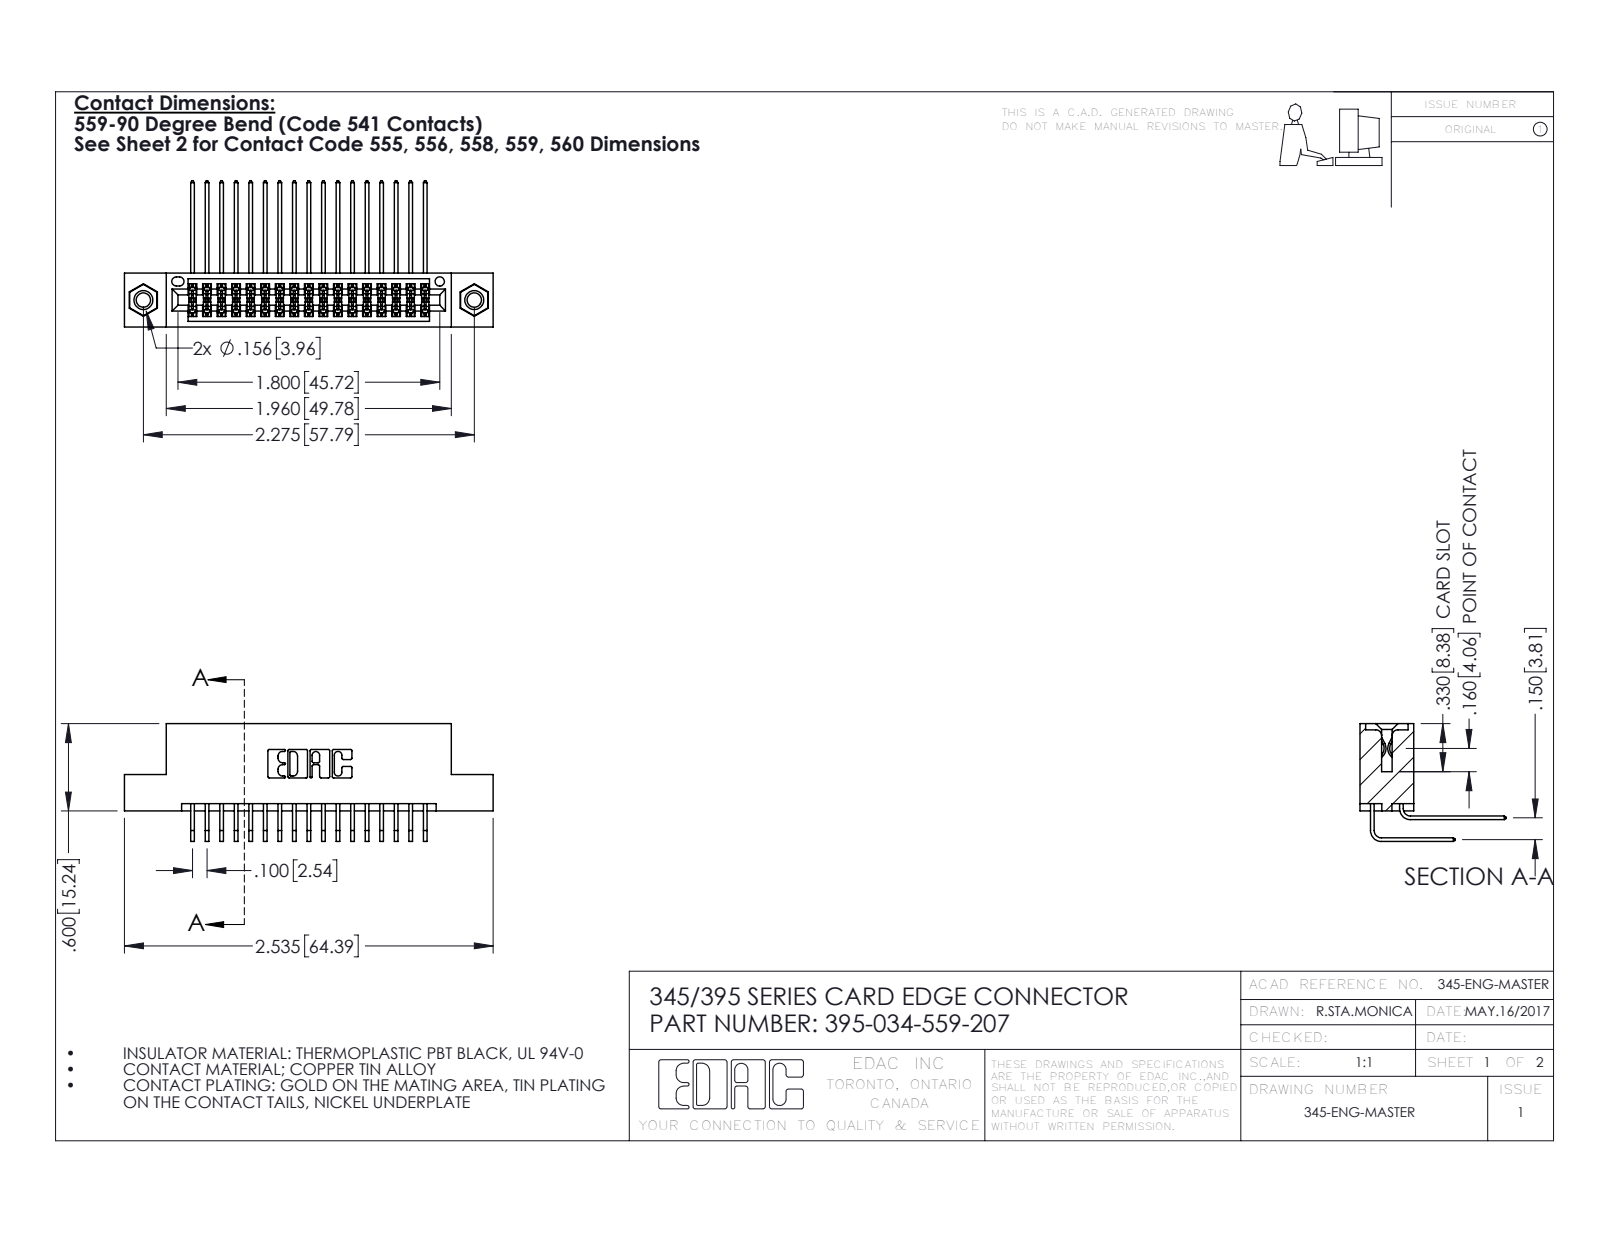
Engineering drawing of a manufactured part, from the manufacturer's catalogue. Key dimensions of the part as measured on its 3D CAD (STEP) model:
Part name (STEP PRODUCT): 345-250-001_345-250-005-103; 345 Part_Flush Mounting Lugs - 0.156 Dia-TI; 395-034-559-207; 345-292-001_558 559 Tail - 1 (+1 more)
STEP written by: SolidWorks 2016 (CONFIG_CONTROL_DESIGN)
Units: inches
Bodies: 37 solids, 1954 faces (1302 planar, 636 cylindrical, 16 other)
Overall size (bounding box): 2.535 × 1.005 × 0.809
Volume: 0.379 in³ · Surface area: 14.94 in²
Round holes (diameter × count): ⌀0.098 ×2, ⌀0.125 ×2, ⌀0.156 ×2, ⌀0.064 ×1
Round bosses / shafts (diameter × count): ⌀0.155 ×2
Partial cylindrical surfaces — rounded edges, fillets, slot ends (radius × count): R0.006 ×52, R0.01 ×22, R0.007 ×6, R0.031 ×6, R0.026 ×3, R0.014 ×2, R0.019 ×2, R0.022 ×2
Main face-to-face distances: 0.072, 0.298, 0.2, 0.37, 0.098, 0.272, 0.025, 0.225, 0.15, 0.175
Hole centre spacings: 0.27, 2.041, 2.275
